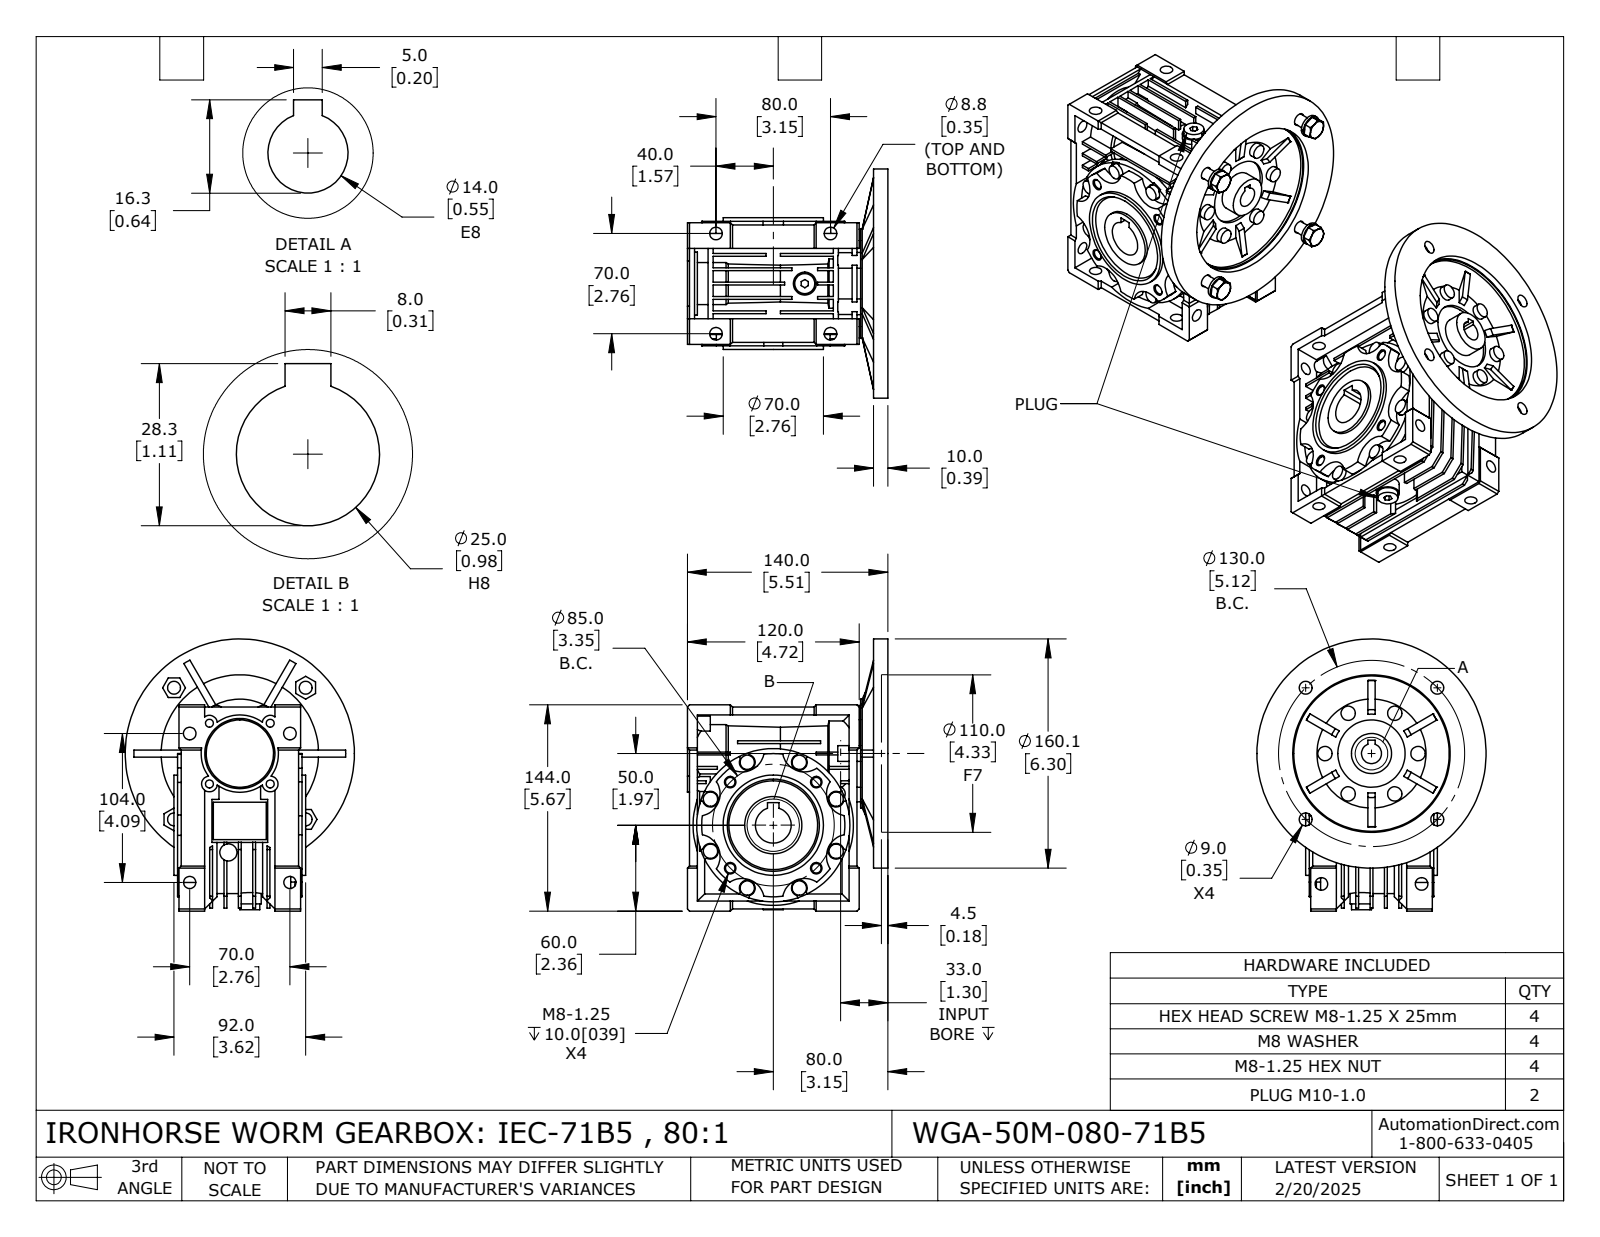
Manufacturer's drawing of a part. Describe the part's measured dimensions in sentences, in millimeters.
The part is named "WGA-50M-080-71B5". Its 3-D file was written by "SolidWorks 2024 (CONFIG_CONTROL_DESIGN)". It is 7 solids with 1007 faces: 577 planar, 316 cylindrical and 114 other. Overall it measures 190.03 by 160.06 by 140 millimeters. Its volume is 1 146 000 cubic millimeters and its surface area 256 628 square millimeters. Round holes: 8 of diameter 8.8, 6 of diameter 8.5, 6 of diameter 9, 4 of diameter 5.55, 2 of diameter 6.65, 2 of diameter 6.65, 1 of diameter 14, 1 of diameter 15, 1 of diameter 25, 1 of diameter 28, 1 of diameter 34, 1 of diameter 40. Round bosses or shafts: 14 of diameter 10, 2 of diameter 16, 2 of diameter 14, 2 of diameter 9.8, 2 of diameter 8.3, 1 of diameter 160.06, 1 of diameter 107, 1 of diameter 76. Partial cylindrical surfaces (rounded edges, fillets, slot ends): 18 of radius 5.5, 8 of radius 6, 8 of radius 15, 8 of radius 15.5, 1 of radius 20.76, 1 of radius 46, 1 of radius 47.7, 1 of radius 50. The main face-to-face distances are 10, 2, 7, 5.5, 8, 1.5, 20, 5, 55, 35. The hole center spacings are 71.58, 70, 30, 35, 42.42, 42.5, 60.1, 65.
